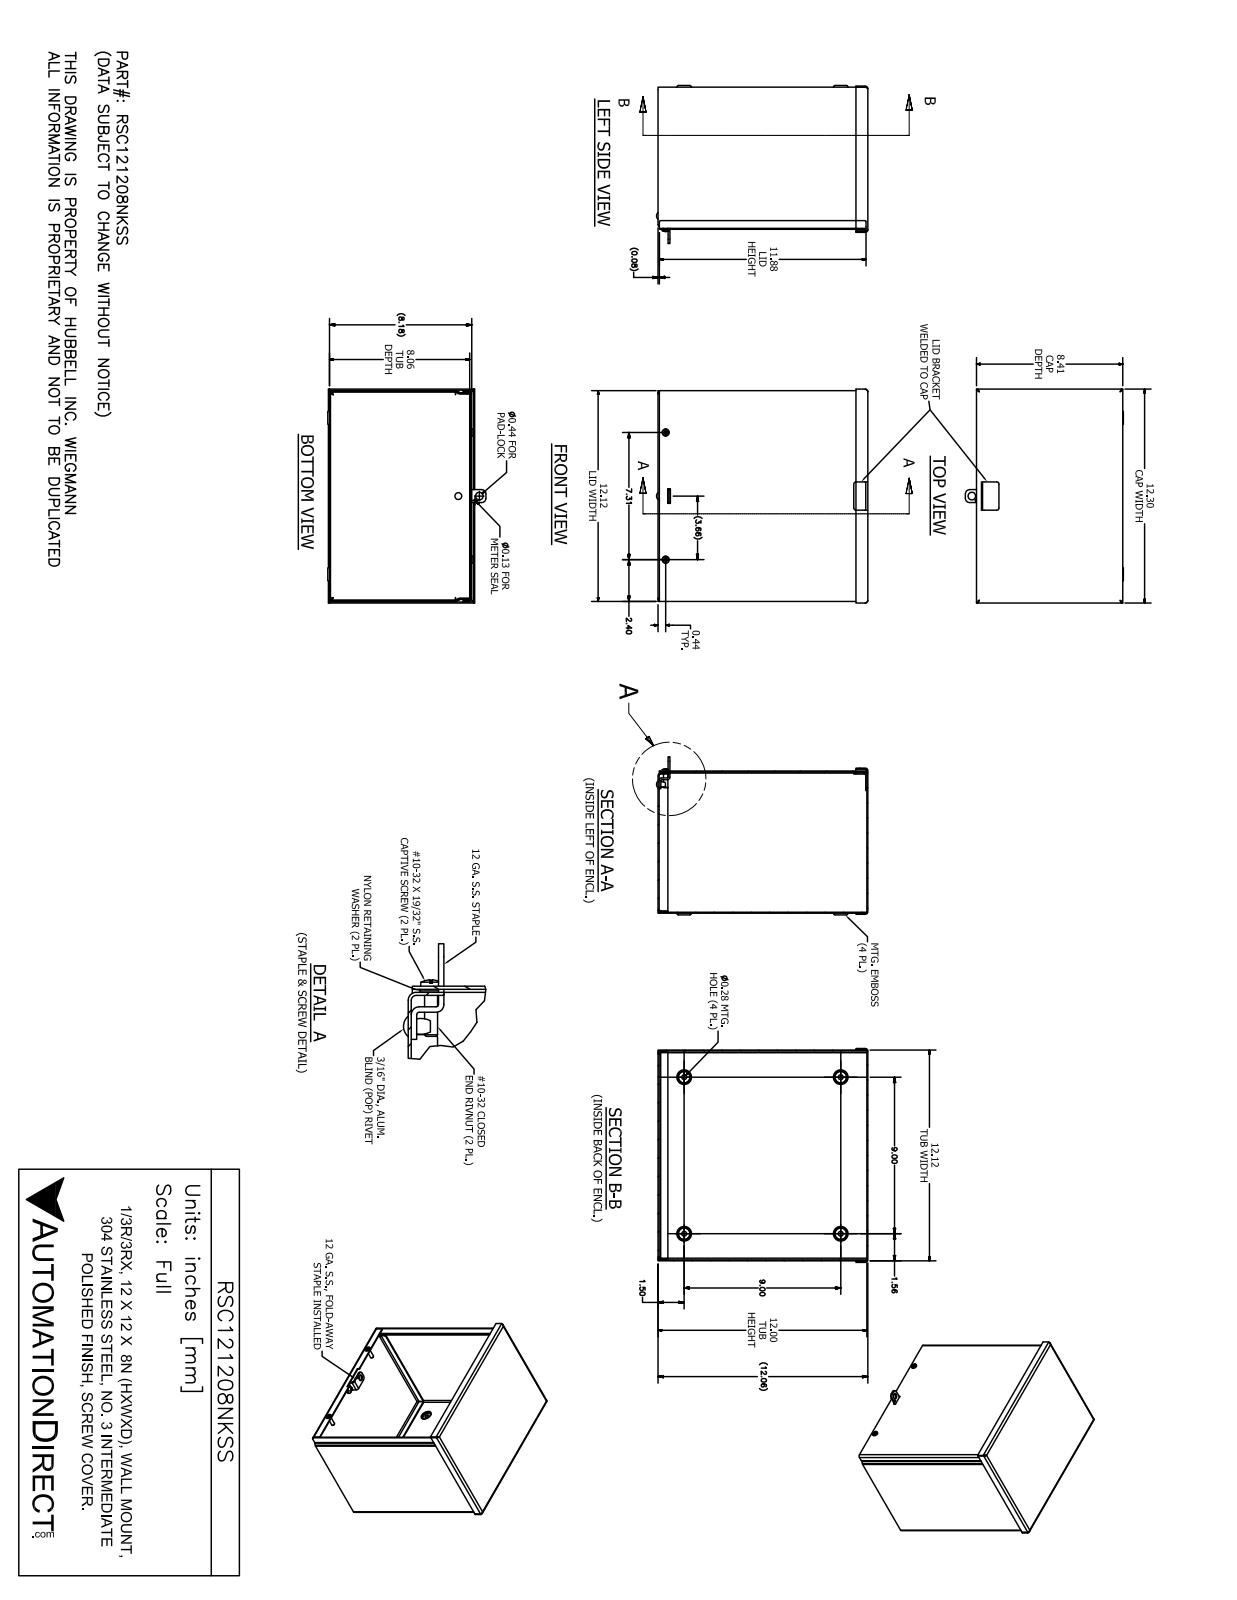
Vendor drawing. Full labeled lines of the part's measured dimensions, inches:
Part name (STEP PRODUCT): RSC121208NKSS
STEP written by: SolidWorks 2017 (AUTOMOTIVE_DESIGN)
Units: inches
Bodies: 13 solids, 383 faces (199 planar, 99 cylindrical, 85 other)
Overall size (bounding box): 12.299 × 12.149 × 9.084
Volume: 43.55 in³ · Surface area: 1 489 in²
Round holes (diameter × count): ⌀0.25 ×4, ⌀0.281 ×4, ⌀0.156 ×2, ⌀0.196 ×2, ⌀0.257 ×2, ⌀0.278 ×2, ⌀0.125 ×1, ⌀0.198 ×1, ⌀0.201 ×1, ⌀0.437 ×1
Round bosses / shafts (diameter × count): ⌀0.453 ×2, ⌀0.406 ×2, ⌀0.248 ×2, ⌀0.167 ×2, ⌀0.187 ×1
Partial cylindrical surfaces — rounded edges, fillets, slot ends (radius × count): R0.094 ×17, R0.153 ×17, R0.031 ×6, R0.125 ×4, R0.25 ×4, R0.047 ×2, R0.05 ×2, R0.062 ×2
Main face-to-face distances: 0.059, 8.117, 12, 12.059, 8.176, 8.058, 11.941, 12.118, 0.059, 0.117
Hole centre spacings: 9, 1.357, 1.381, 7.313, 8.225, 8.229, 10.098, 10.129
